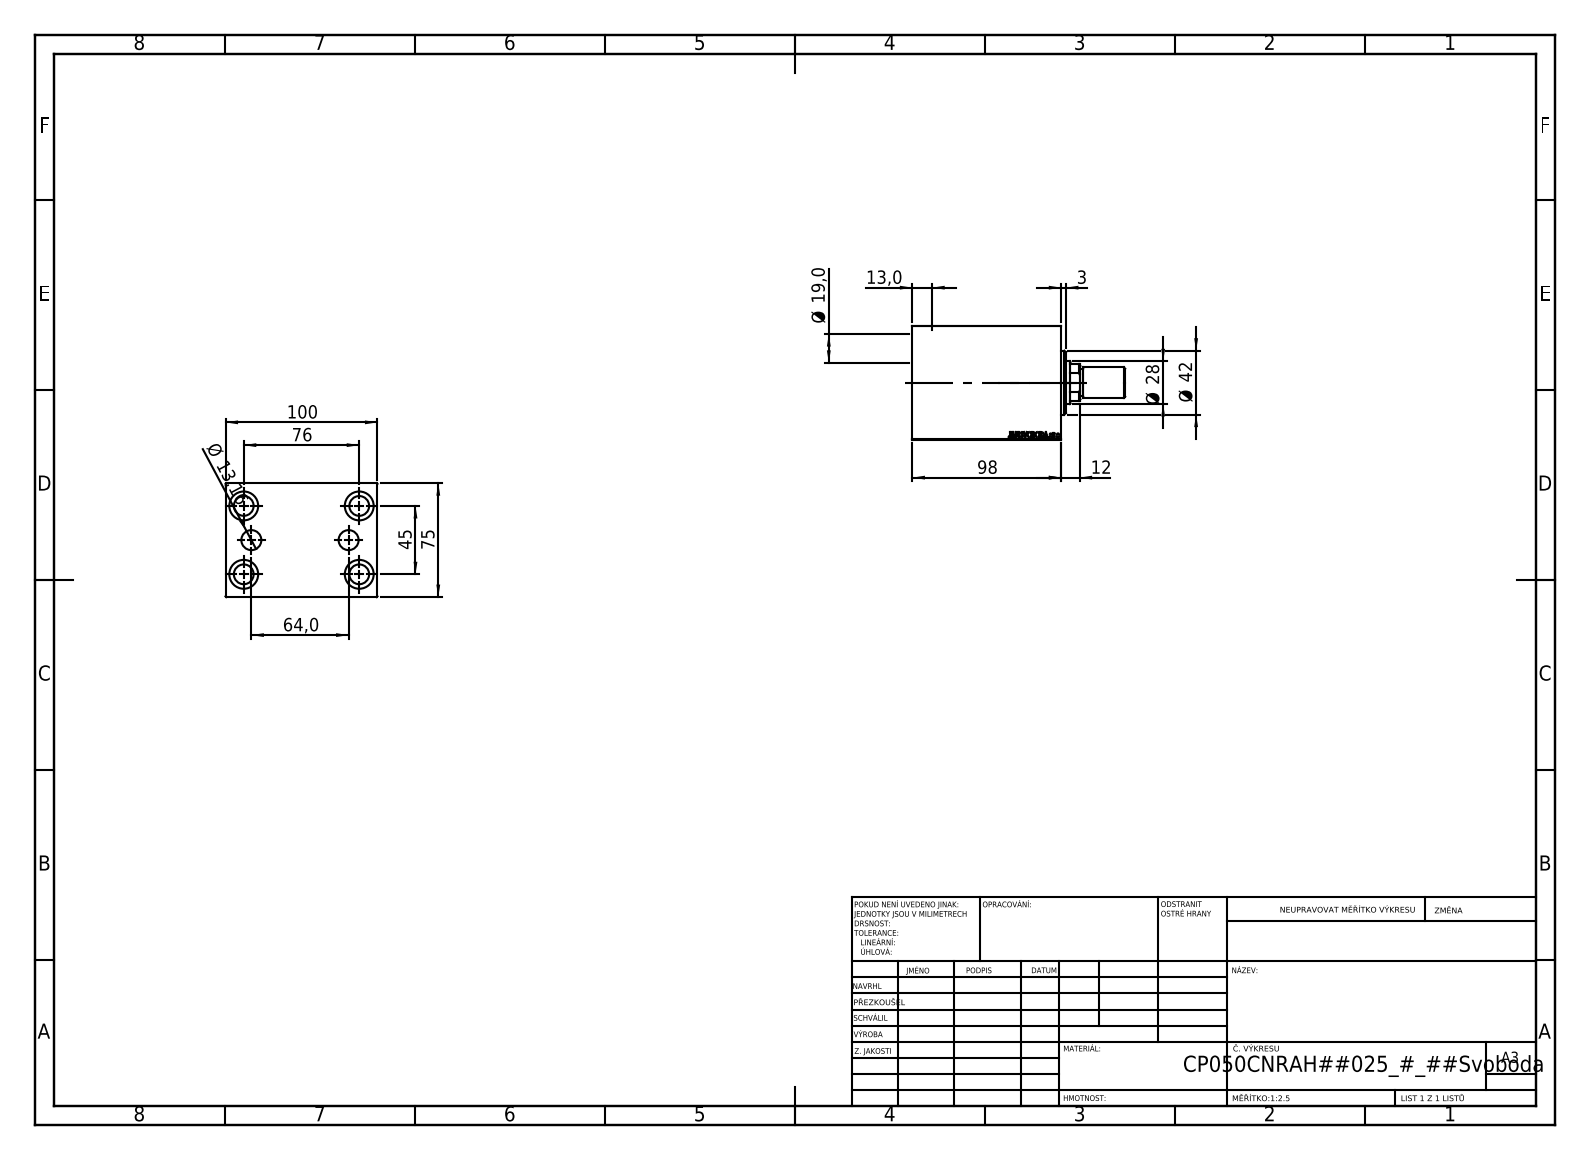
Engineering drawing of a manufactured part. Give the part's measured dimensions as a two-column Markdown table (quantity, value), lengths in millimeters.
| quantity | value |
| --- | --- |
| part name | V450CM_MALE_METRIC; V450CM_C_VCP; V450CM_VC_B; V450CM_C_Body |
| STEP written by | SolidWorks 2019 (CONFIG_CONTROL_DESIGN) |
| units | millimeters |
| bodies | 4 solids, 869 faces (411 planar, 58 cylindrical, 400 other) |
| overall size | 140 × 100 × 75 |
| volume | 641 636 mm³ |
| surface area | 107 688 mm² |
| round holes (diameter × count) | 13 × 4, 19 × 4, 13.16 × 2, 18.5 × 1, 28 × 1, 31.5 × 1, 50 × 1, 52 × 1, 57 × 1 |
| round bosses / shafts (diameter × count) | 42 × 1, 20 × 1, 18 × 1 |
| partial cylindrical surfaces (radius × count) | 13.5 × 1 |
| main face-to-face distances | 75, 100, 98, 84, 14, 12, 72, 25, 86, 47 |
| hole center spacings | 44.16, 23.05, 23.56, 45, 72.58, 74.48, 76, 88.32 |
